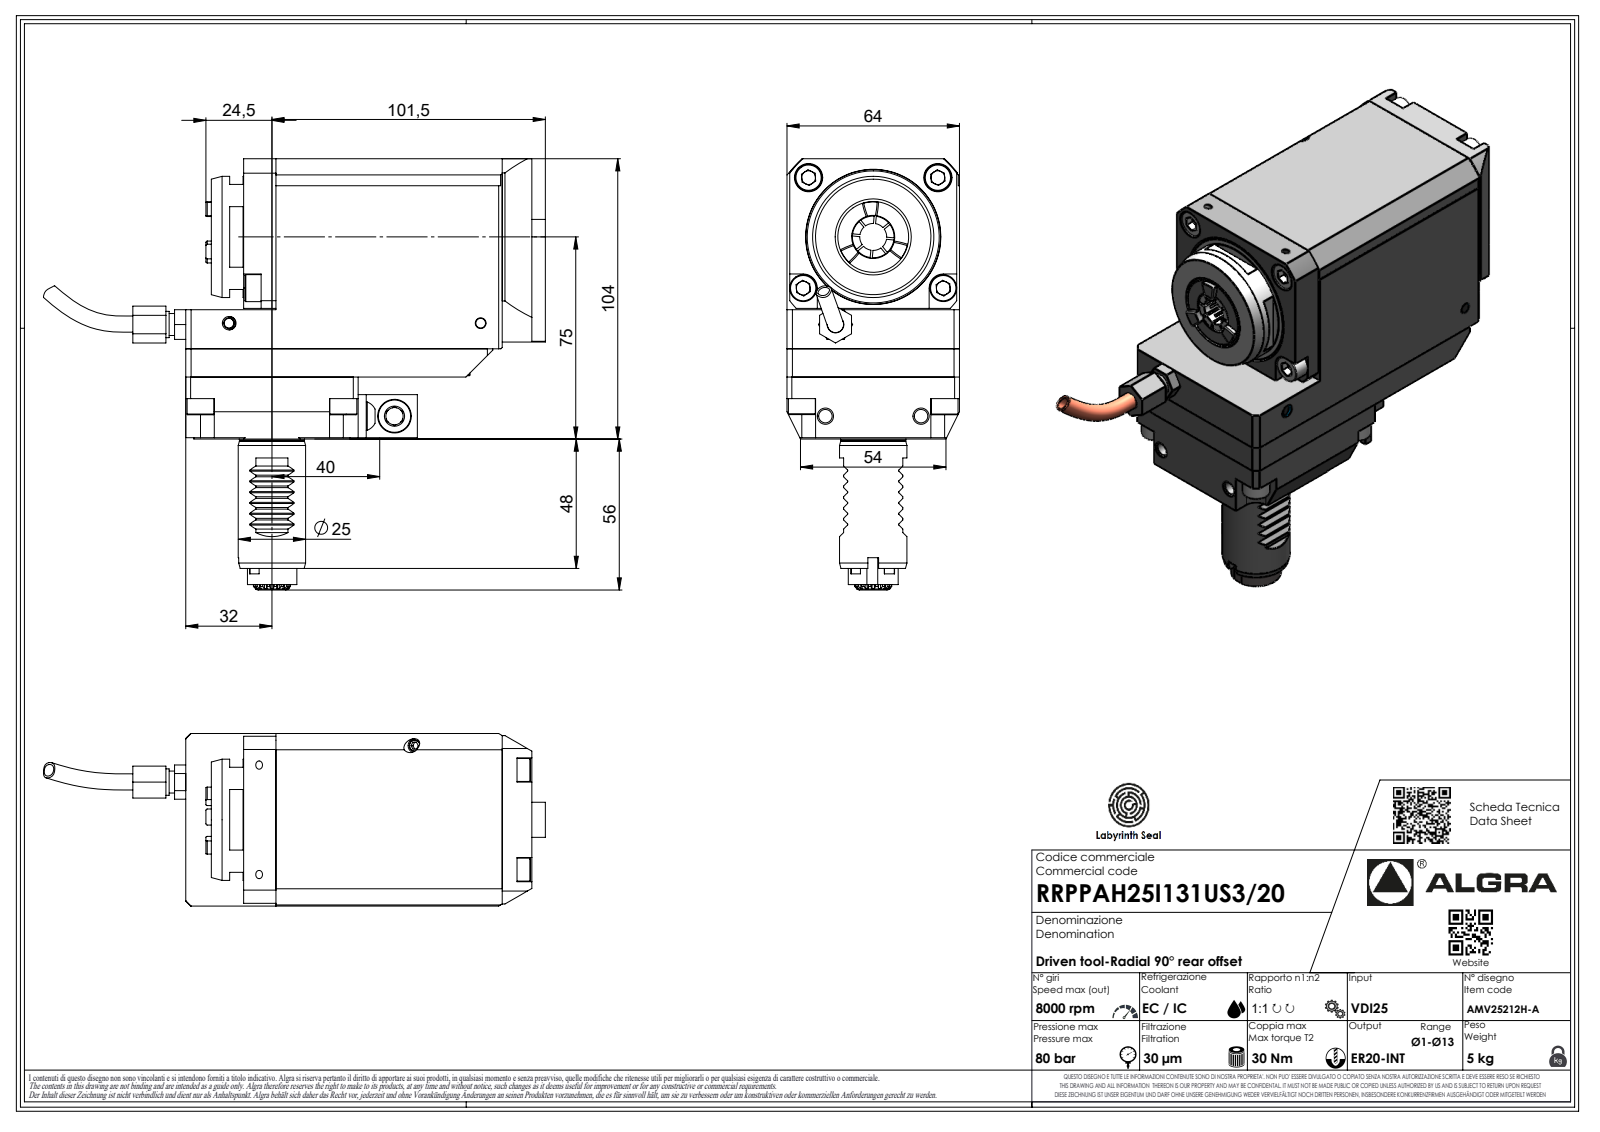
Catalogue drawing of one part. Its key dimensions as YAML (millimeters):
part_name: "RRPPAH25I131US320"
step_written_by: "SolidWorks 2023 (AUTOMOTIVE_DESIGN)"
units: millimeters
bodies: {solids: 1, faces: 742, planar: 482, cylindrical: 123, other: 137}
overall_size: [186.31, 160, 64]
volume: 708865
surface_area: 60878
round_holes:
  - {diameter: 2.1, count: 1}
  - {diameter: 9, count: 1}
round_bosses_or_shafts:
  - {diameter: 45, count: 1}
  - {diameter: 25, count: 1}
  - {diameter: 24.1, count: 1}
  - {diameter: 18.5, count: 1}
  - {diameter: 9.8, count: 1}
  - {diameter: 8.15, count: 1}
  - {diameter: 6.37, count: 1}
  - {diameter: 1.7, count: 1}
partial_cylinders:
  - {radius: 0.3, count: 12}
  - {radius: 0.33, count: 7}
  - {radius: 0.52, count: 7}
  - {radius: 3.7, count: 7}
  - {radius: 32.53, count: 5}
  - {radius: 5.25, count: 2}
  - {radius: 0.21, count: 1}
  - {radius: 6.15, count: 1}
face_to_face_distances: [64, 104, 48, 128.5, 25, 81, 23, 56, 107, 21.5]
